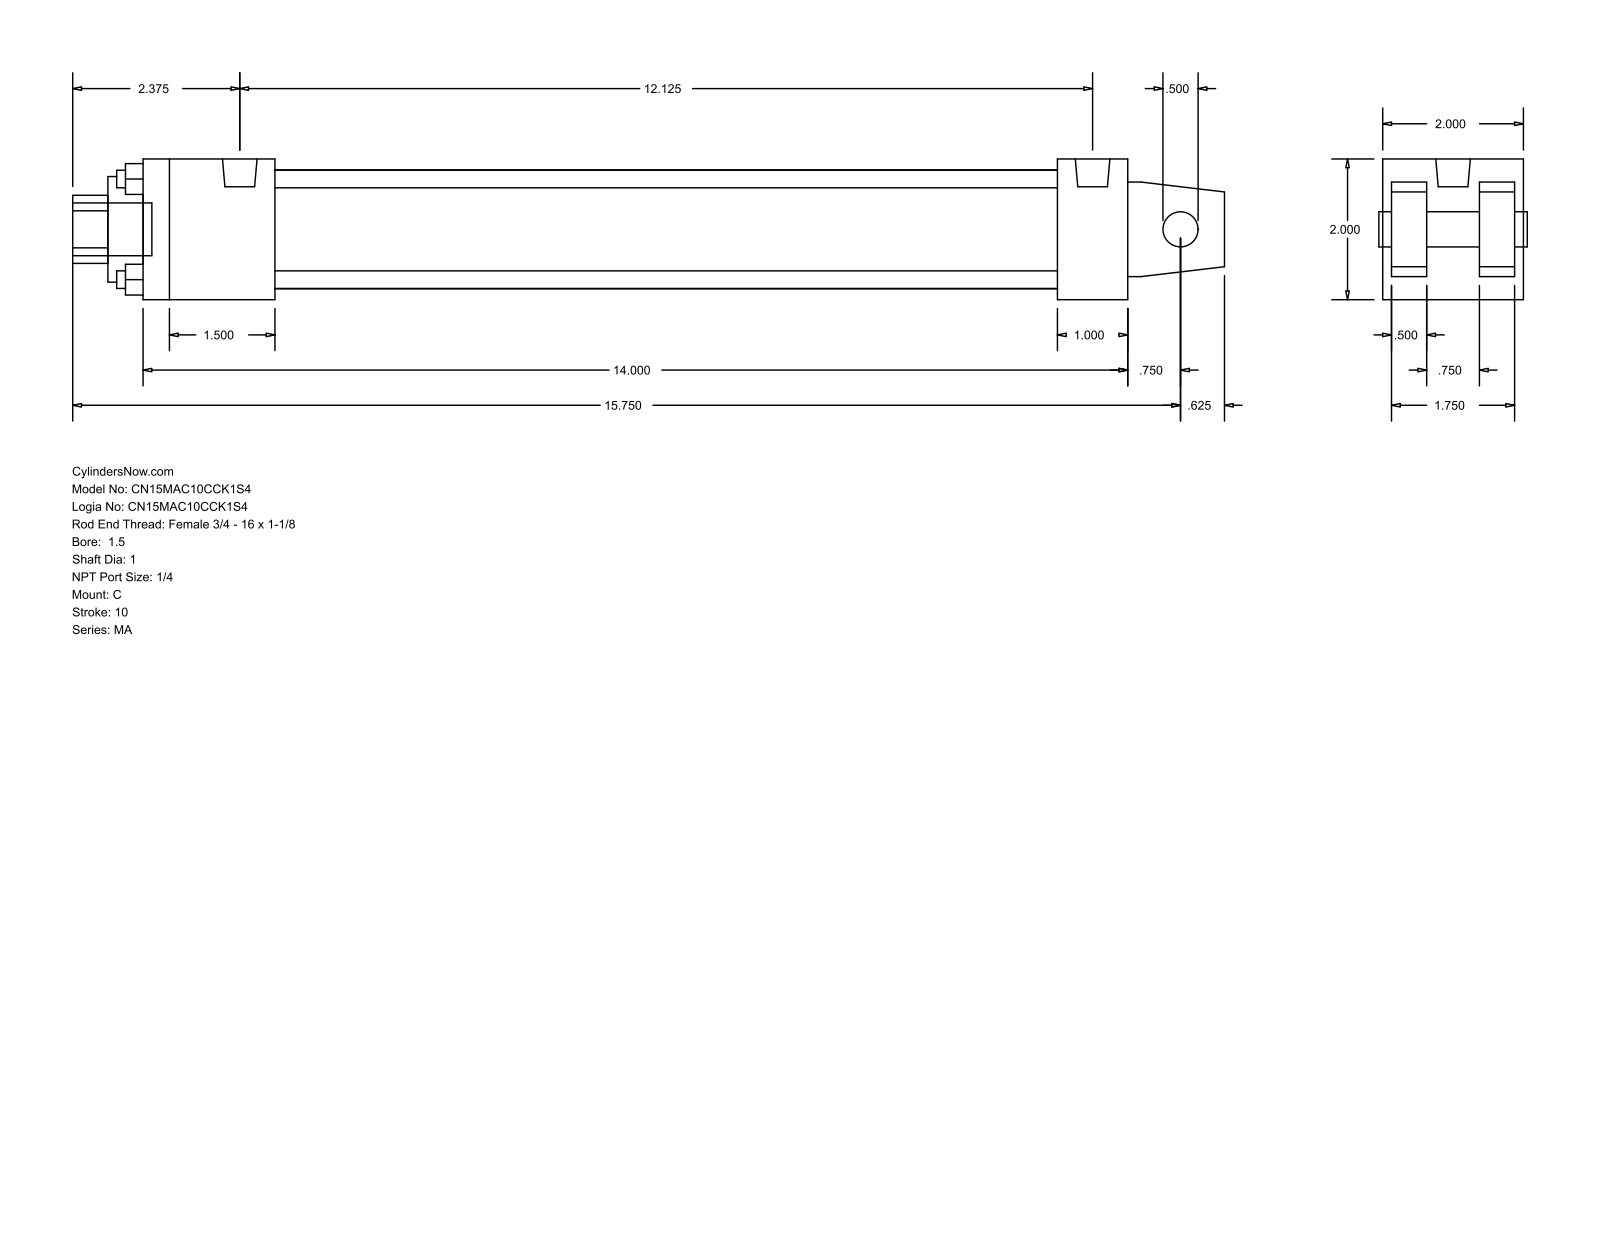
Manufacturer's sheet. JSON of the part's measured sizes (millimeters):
{"part_name": "MA_C__0150_1", "step_written_by": "GSSL Pune (CONFIG_CONTROL_DESIGN)", "units": "millimeters", "bodies": {"solids": 0, "faces": 103, "planar": 76, "cylindrical": 27, "other": 0}, "overall_size": [415.93, 50.8, 50.8], "round_holes": [[6.35, 4], [12.7, 1], [25.4, 1], [38.1, 1], [42.93, 1]], "round_bosses_or_shafts": [[7.94, 4], [12.49, 2], [19.05, 1]], "partial_cylinders_radius": [[12.29, 1]], "face_to_face_distances": [50.8, 47.63, 12.7, 34.93, 3.17, 15.87, 31.76, 60.33, 342.9, 44.46], "hole_center_spacings": [25.68, 36.32, 51.36]}
